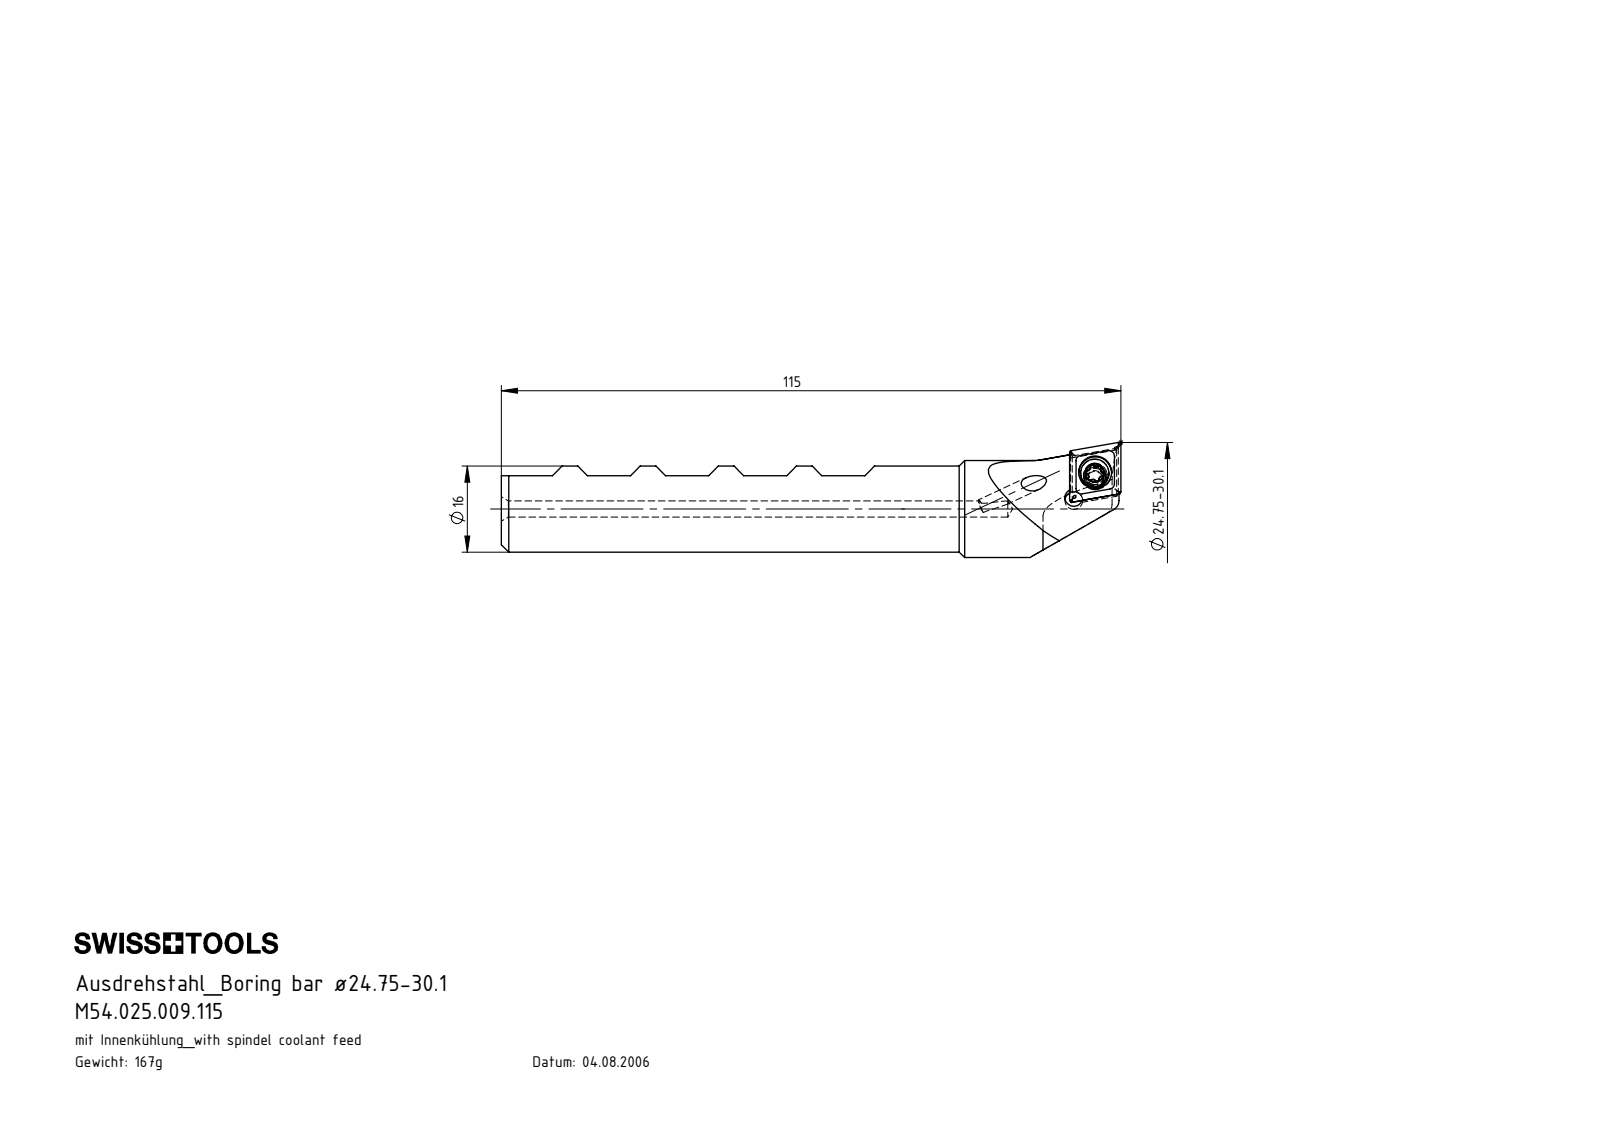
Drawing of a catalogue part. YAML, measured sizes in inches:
part_name: "WCB-ER2.001.009_A; CCMT09T304; B25.WCB.K11.115; B25-WCB.K11.115_B"
step_written_by: "SolidWorks 2017 (AUTOMOTIVE_DESIGN)"
units: inches
bodies: {solids: 3, faces: 117, planar: 45, cylindrical: 26, other: 46}
overall_size: [4.528, 0.842, 0.75]
volume: 1.296
surface_area: 11.79
round_holes:
  - {diameter: 0.118, count: 2}
  - {diameter: 0.13, count: 2}
  - {diameter: 0.173, count: 1}
  - {diameter: 0.24, count: 1}
round_bosses_or_shafts:
  - {diameter: 0.709, count: 1}
  - {diameter: 0.63, count: 1}
  - {diameter: 0.207, count: 1}
  - {diameter: 0.157, count: 1}
partial_cylinders:
  - {radius: 0.013, count: 6}
  - {radius: 0.023, count: 6}
  - {radius: 0.079, count: 1}
  - {radius: 0.362, count: 1}
  - {radius: 0.472, count: 1}
face_to_face_distances: [0.404, 0.274, 0.807, 1.211, 0.807, 0.422, 0.148, 0.43, 0.156, 1.211]
hole_center_spacings: [0.239, 0.244]
